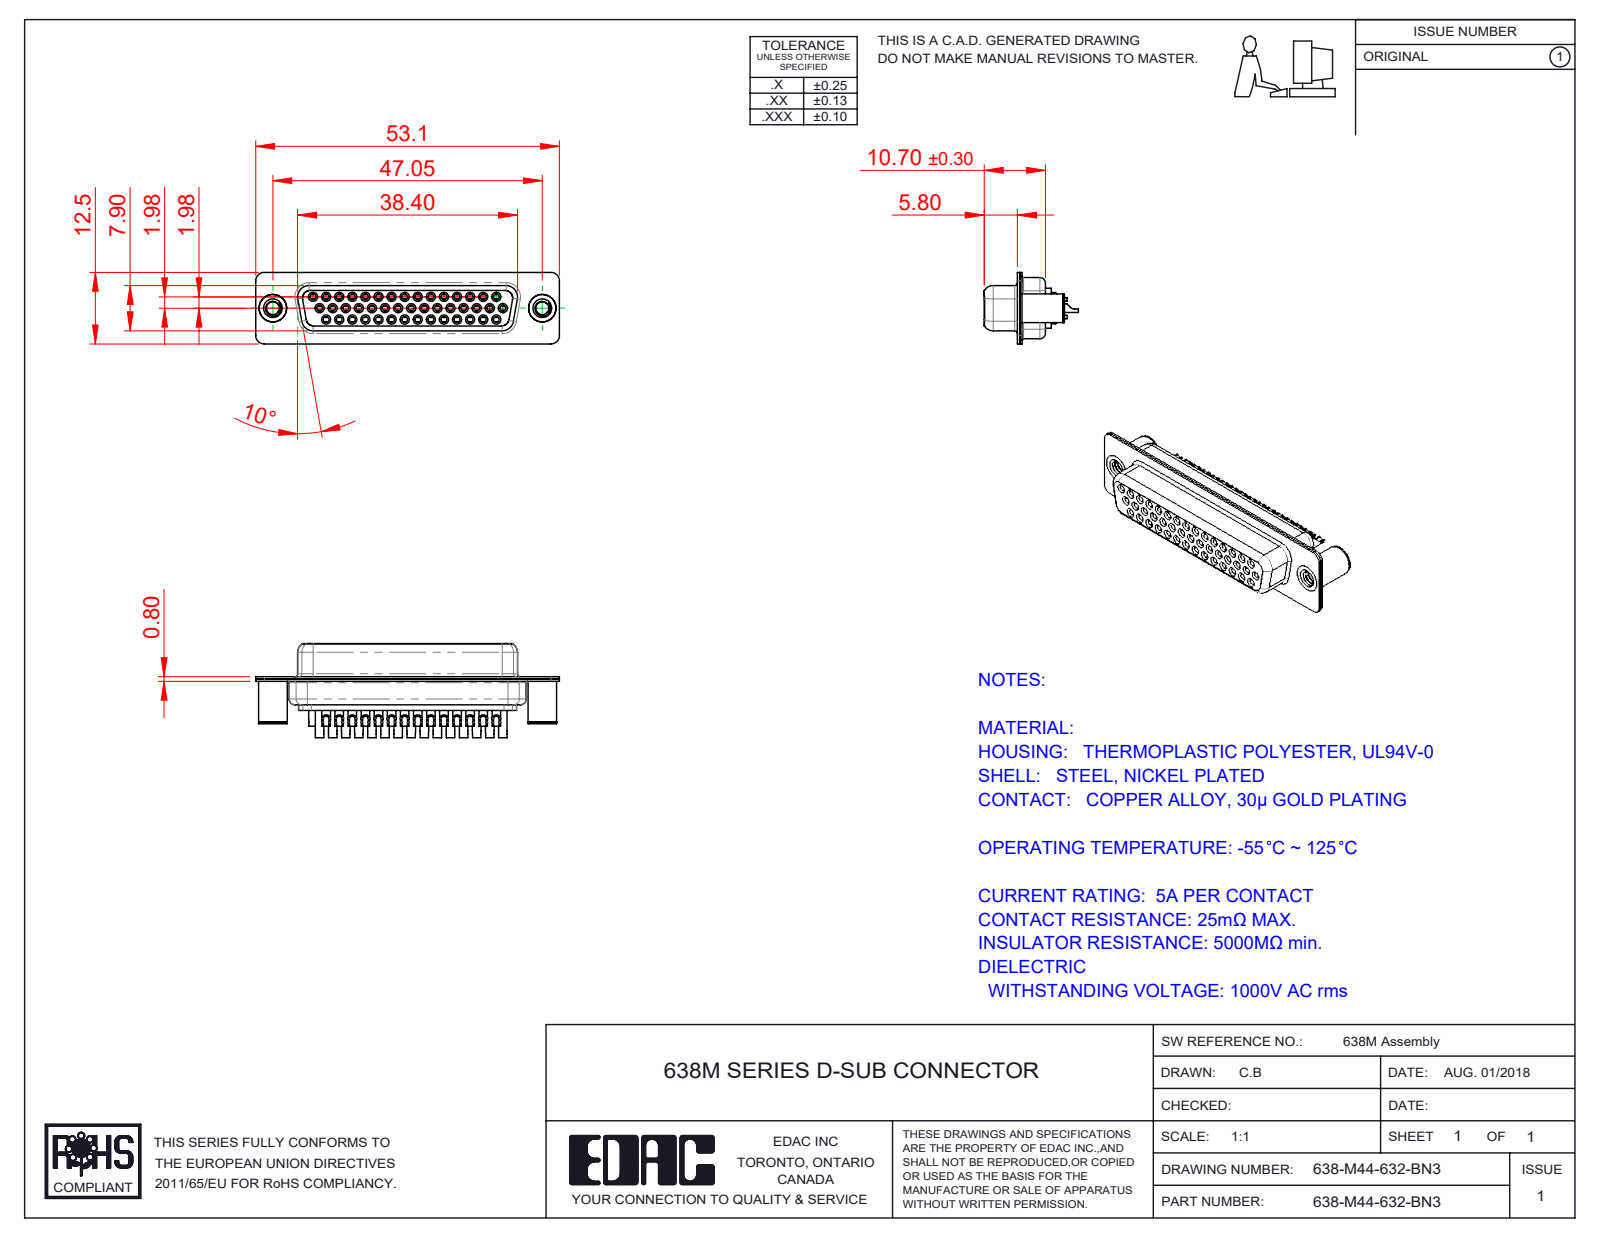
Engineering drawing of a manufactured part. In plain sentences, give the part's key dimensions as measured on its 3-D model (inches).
The part is named "638M 4-40 Threaded Board Spacer; 638M Shell Front_44 Contacts; 638-M44-632-BN3; 638M Shell Rear_44 Contacts (+4 more)". Its 3-D file was written by "SolidWorks 2020 (CONFIG_CONTROL_DESIGN)". It is 49 solids with 2733 faces: 815 planar, 1085 cylindrical and 833 other. Overall it measures 2.089 by 0.648 by 0.492 inches. Its volume is 0.227 cubic inches and its surface area 19.51 square inches. Round holes: 44 of diameter 0.039, 44 of diameter 0.043, 44 of diameter 0.067, 44 of diameter 0.071, 44 of diameter 0.079, 2 of diameter 0.089, 2 of diameter 0.128, 2 of diameter 0.157, 2 of diameter 0.189. Round bosses or shafts: 44 of diameter 0.087, 44 of diameter 0.063, 44 of diameter 0.059, 2 of diameter 0.197, 2 of diameter 0.193. Partial cylindrical surfaces (rounded edges, fillets, slot ends): 16 of radius 0.059, 12 of radius 0.079, 9 of radius 0.053, 8 of radius 0.063, 7 of radius 0.039, 4 of radius 0.01, 4 of radius 0.02, 4 of radius 0.024. The main face-to-face distances are 0.016, 0.055, 0.018, 0.333, 0.35, 0.071, 0.039, 0.244, 0.278, 0.073. The hole center spacings are 0.09, 0.09, 0.156, 0.18, 0.324, 0.27, 0.45, 0.59.
